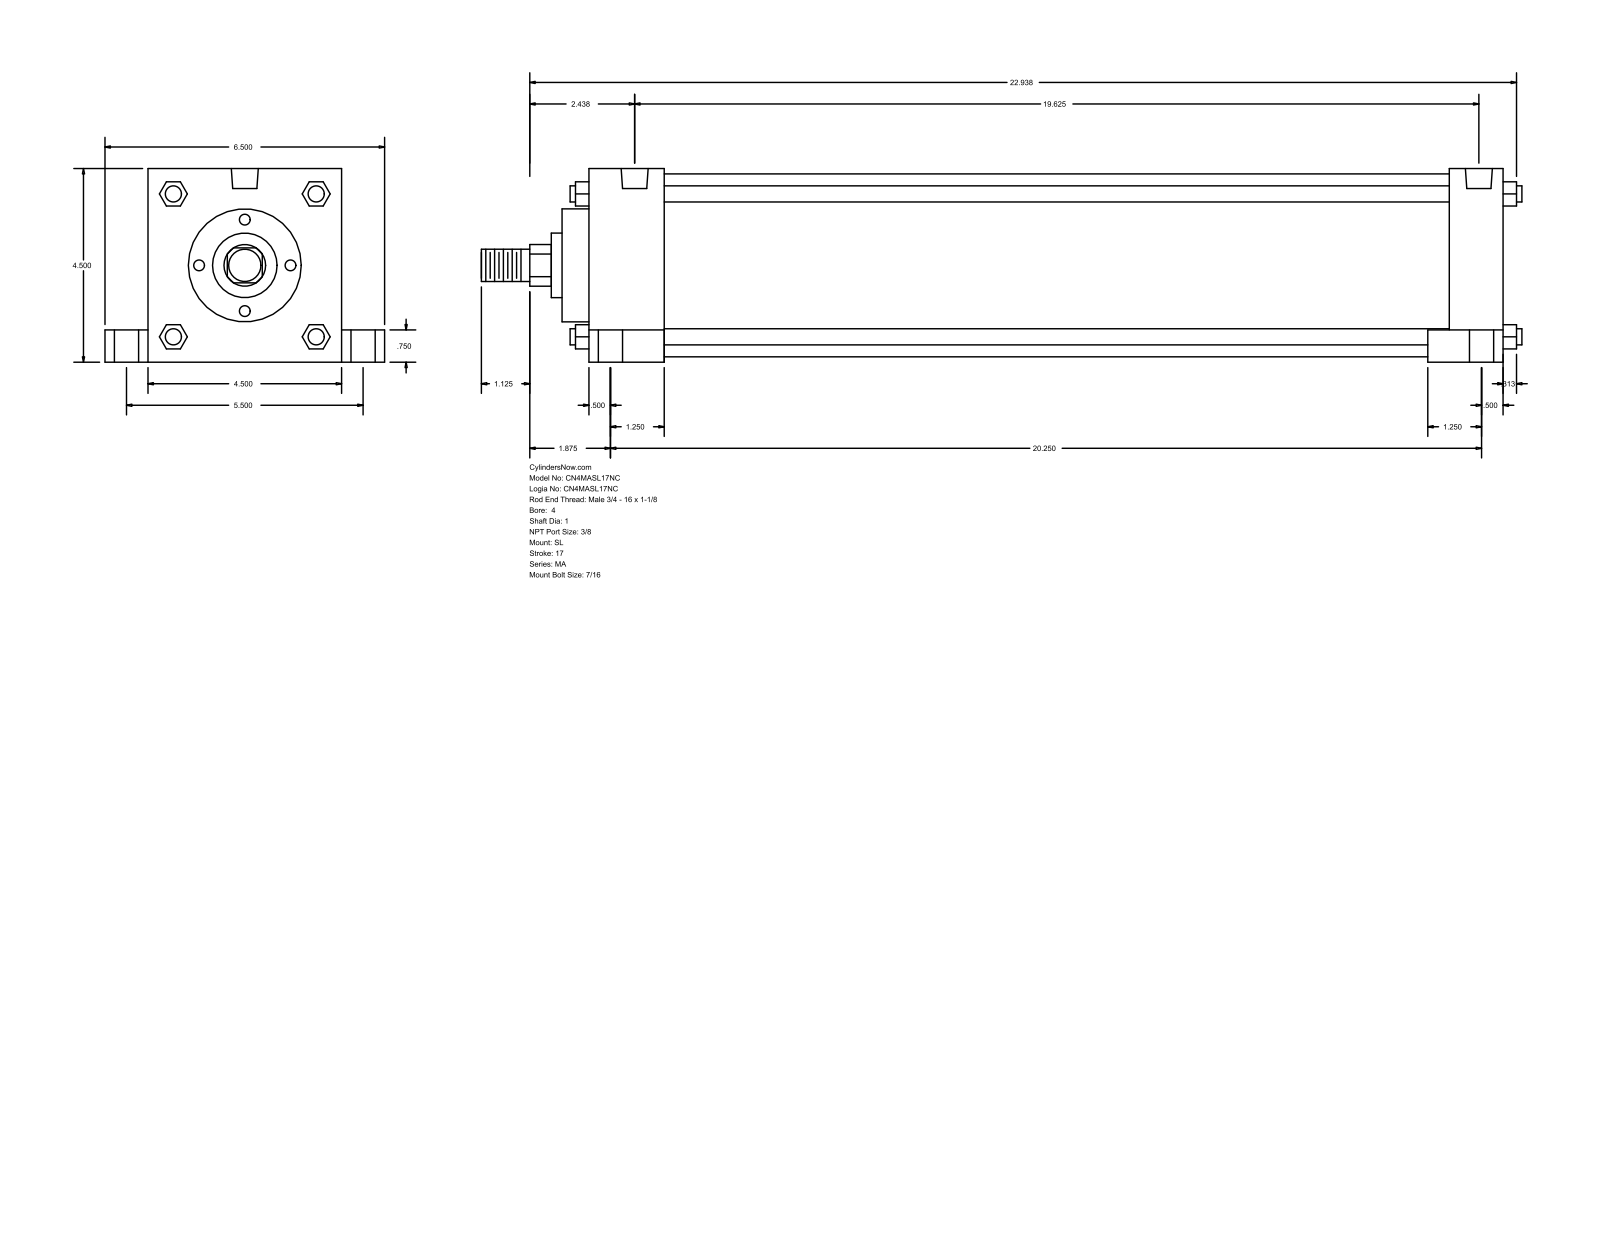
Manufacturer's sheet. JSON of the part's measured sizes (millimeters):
{"part_name": "MA_SL__0400_1", "step_written_by": "GSSL Pune (CONFIG_CONTROL_DESIGN)", "units": "millimeters", "bodies": {"solids": 0, "faces": 150, "planar": 113, "cylindrical": 37, "other": 0}, "overall_size": [614.36, 165.1, 114.3], "round_holes": [[11.11, 4], [14.29, 4], [20.64, 4], [15.93, 2]], "round_bosses_or_shafts": [[9.53, 4], [107.95, 1], [66.67, 1], [38.1, 1], [25.4, 1], [19.05, 1]], "partial_cylinders_radius": [[12.29, 1]], "face_to_face_distances": [114.3, 539.75, 44.46, 495.29, 508, 463.54, 31.75, 25.4, 139.7, 555.62], "hole_center_spacings": [69.87, 70.14, 71.3, 72.4, 139.7, 488.95, 500.21, 504.92]}
